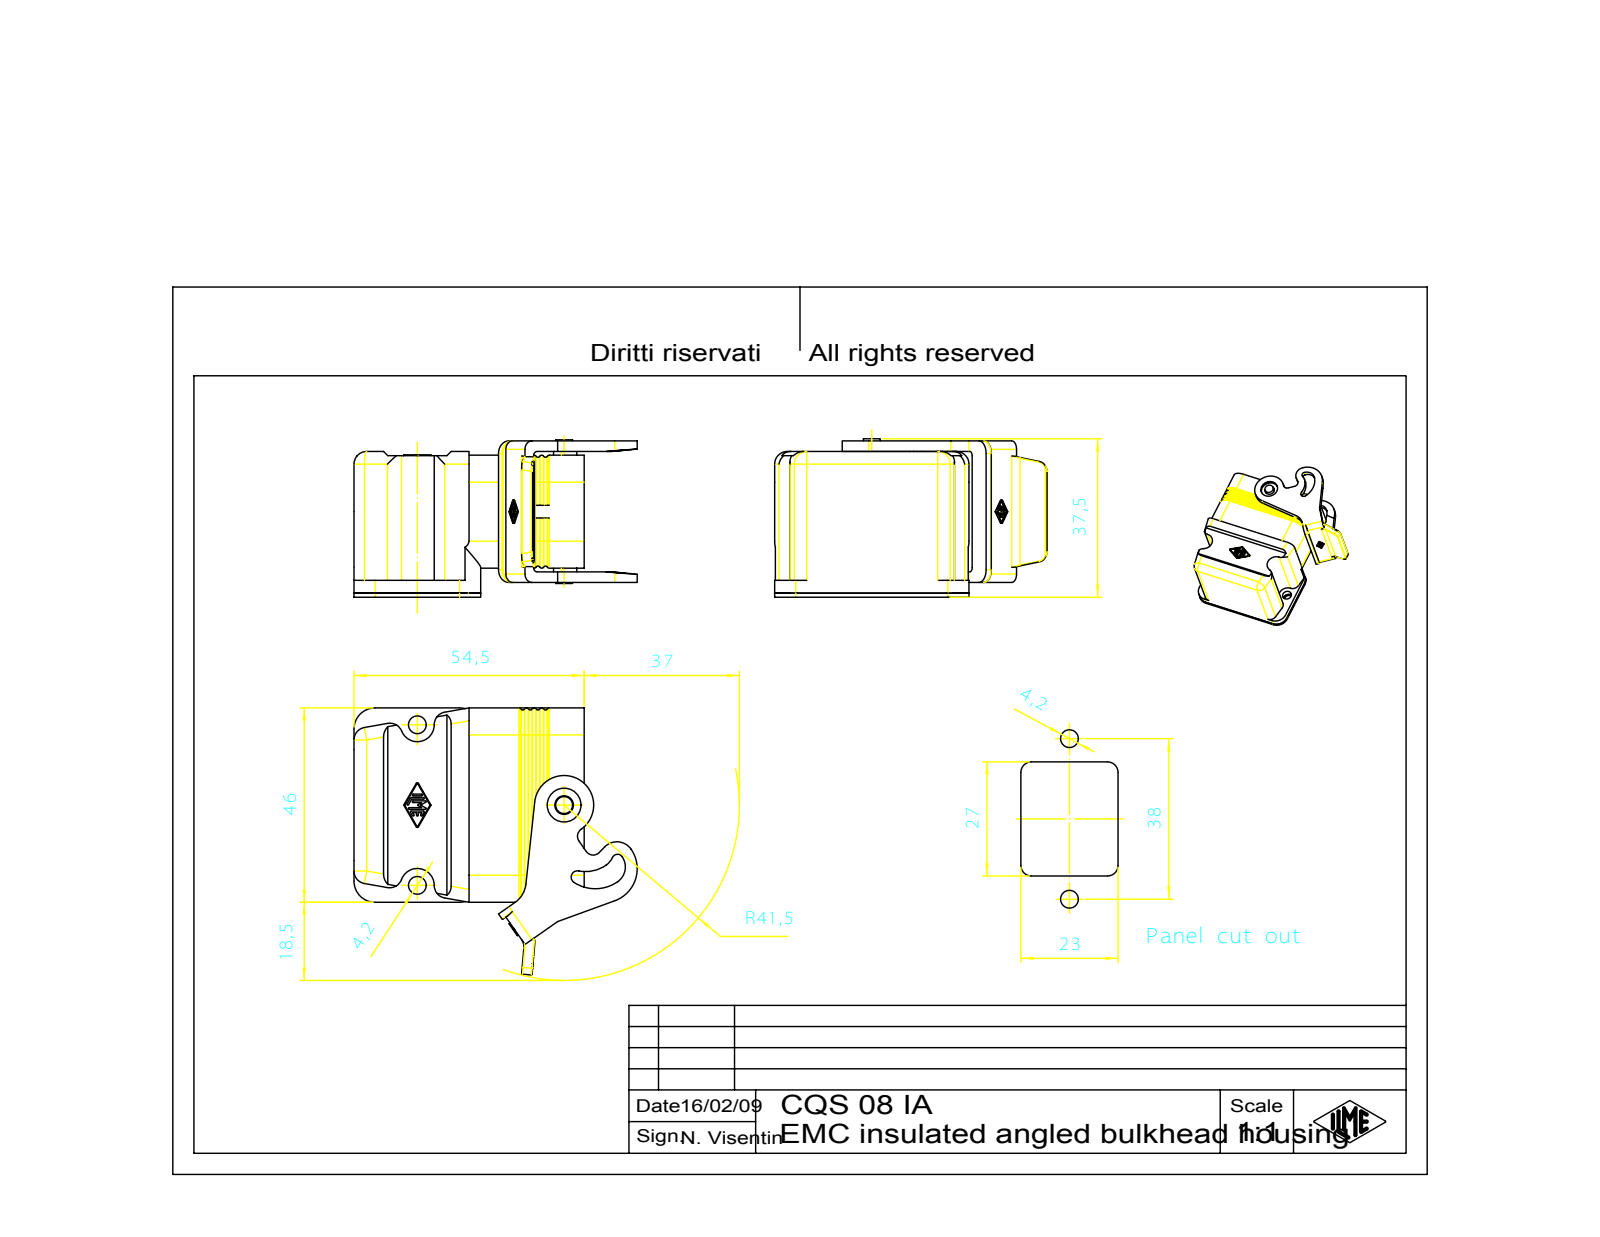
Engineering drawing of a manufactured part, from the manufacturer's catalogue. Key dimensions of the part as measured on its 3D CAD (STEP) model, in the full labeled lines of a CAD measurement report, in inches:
Part name (STEP PRODUCT): CUSTODIA_CQ_08_IA; LEVA_CQ_08_IAP; CQS_08_IA
STEP written by: CoCreate Modeling 16.00A 16-Aug-2008 (C) Parametric Technology GmbH (AUTOMOTIVE_DESIGN)
Units: inches
Bodies: 2 solids, 699 faces (269 planar, 280 cylindrical, 150 other)
Overall size (bounding box): 2.64 × 2.488 × 1.467
Volume: 1.707 in³ · Surface area: 36.92 in²
Round holes (diameter × count): ⌀0.094 ×4, ⌀0.098 ×4, ⌀0.122 ×4, ⌀0.165 ×2, ⌀0.173 ×1, ⌀0.315 ×1
Round bosses / shafts (diameter × count): ⌀0.157 ×1
Partial cylindrical surfaces — rounded edges, fillets, slot ends (radius × count): R0.02 ×36, R0.004 ×14, R0.008 ×13, R0.118 ×13, R0.079 ×9, R0.098 ×5, R0.067 ×4, R0.177 ×4
Main face-to-face distances: 0.098, 1.083, 1.319, 0.108, 1.014, 0.138, 0.207, 1.112, 0.039, 1.22
Hole centre spacings: 0.287, 0.528, 1.268, 1.373, 1.407, 1.273, 1.559, 1.751
